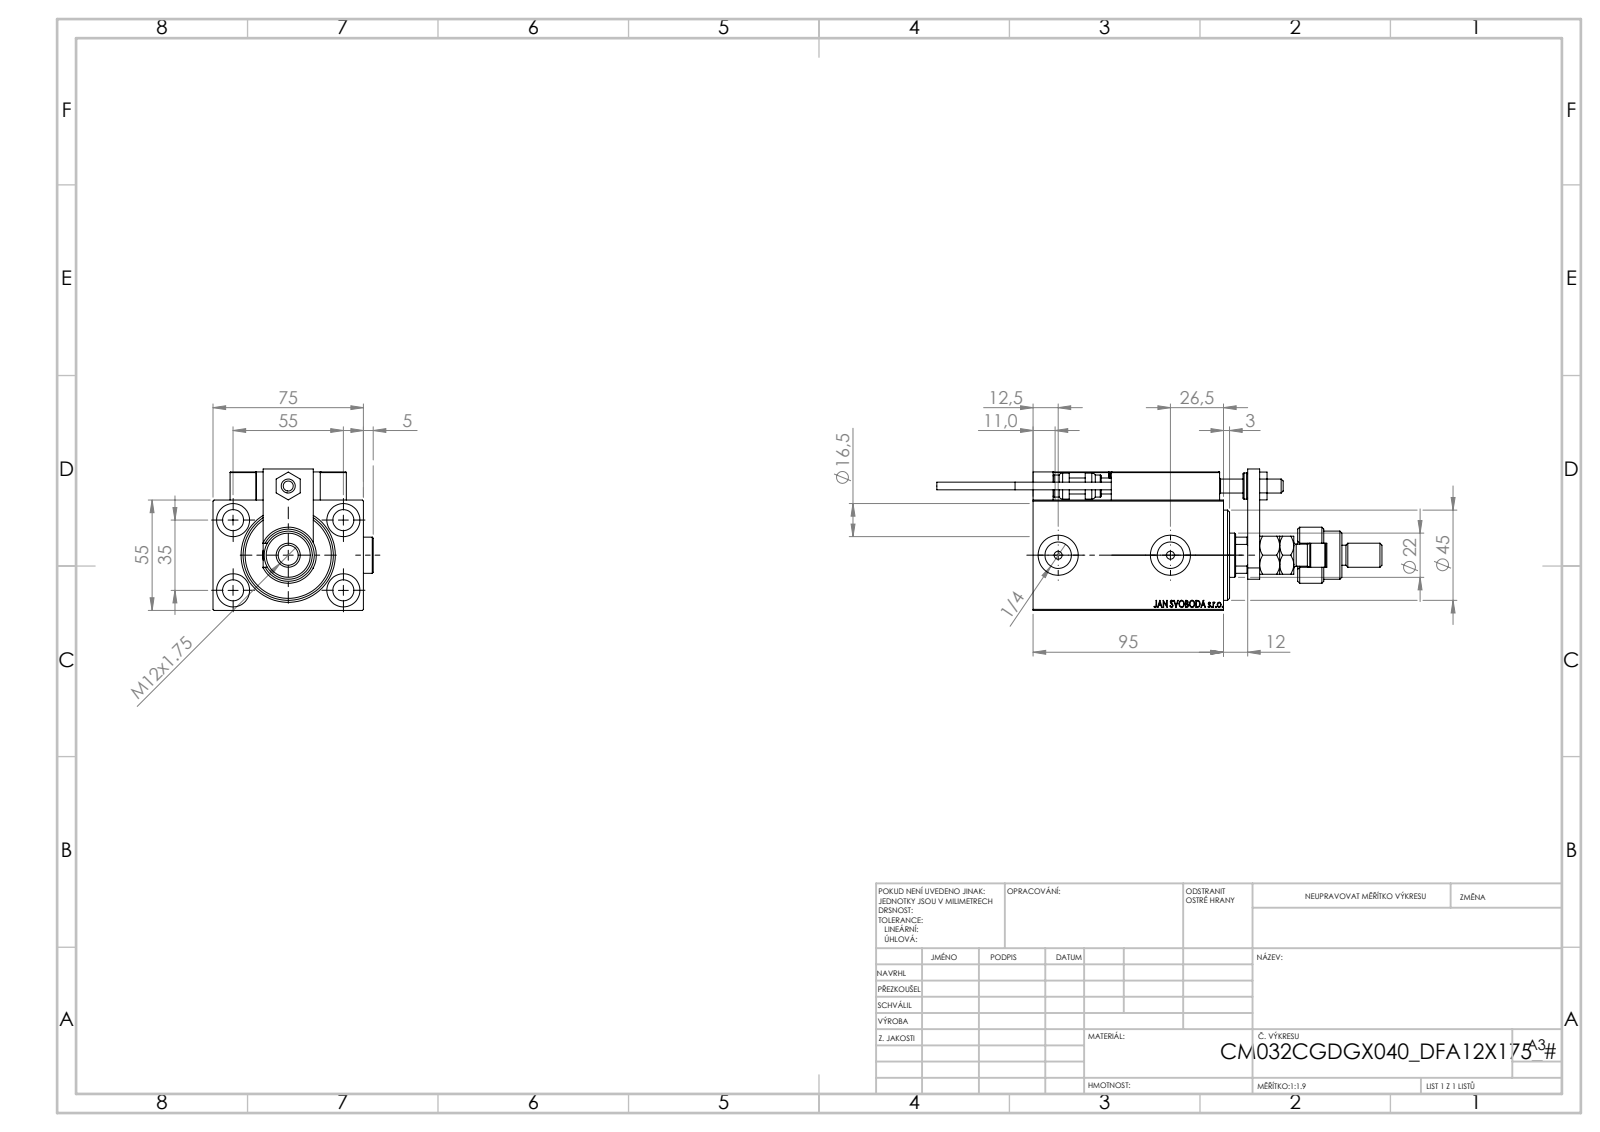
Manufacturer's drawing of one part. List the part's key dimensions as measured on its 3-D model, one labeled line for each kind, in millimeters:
Part name (STEP PRODUCT): TYC_L79; X_Y_DFA; KONCOVKA; FEMALE_PART_FOR_DFA (+7 more)
STEP written by: SolidWorks 2019 (CONFIG_CONTROL_DESIGN)
Units: millimetres
Bodies: 27 solids, 1421 faces (622 planar, 217 cylindrical, 582 other)
Overall size (bounding box): 222 × 79.9 × 70.5
Volume: 397 662 mm³ · Surface area: 106 253 mm²
Round holes (diameter × count): ⌀4 ×6, ⌀8 ×5, ⌀10.5 ×5, ⌀16.5 ×5, ⌀3.2 ×4, ⌀5 ×2, ⌀13.16 ×2, ⌀20 ×2, ⌀7 ×1, ⌀22 ×1, ⌀25.5 ×1, ⌀32 ×1
Round bosses / shafts (diameter × count): ⌀18 ×3, ⌀11 ×2, ⌀5 ×2, ⌀3.8 ×2, ⌀28 ×1, ⌀24 ×1, ⌀13 ×1, ⌀12 ×1
Partial cylindrical surfaces — rounded edges, fillets, slot ends (radius × count): R0.3 ×30, R3 ×2, R9.75 ×1, R10.5 ×1
Main face-to-face distances: 55, 75, 14, 12, 10, 18, 25, 5, 15, 6
Hole centre spacings: 32.6, 11.37, 20, 29.59, 29.69, 32.33, 35, 36.06
